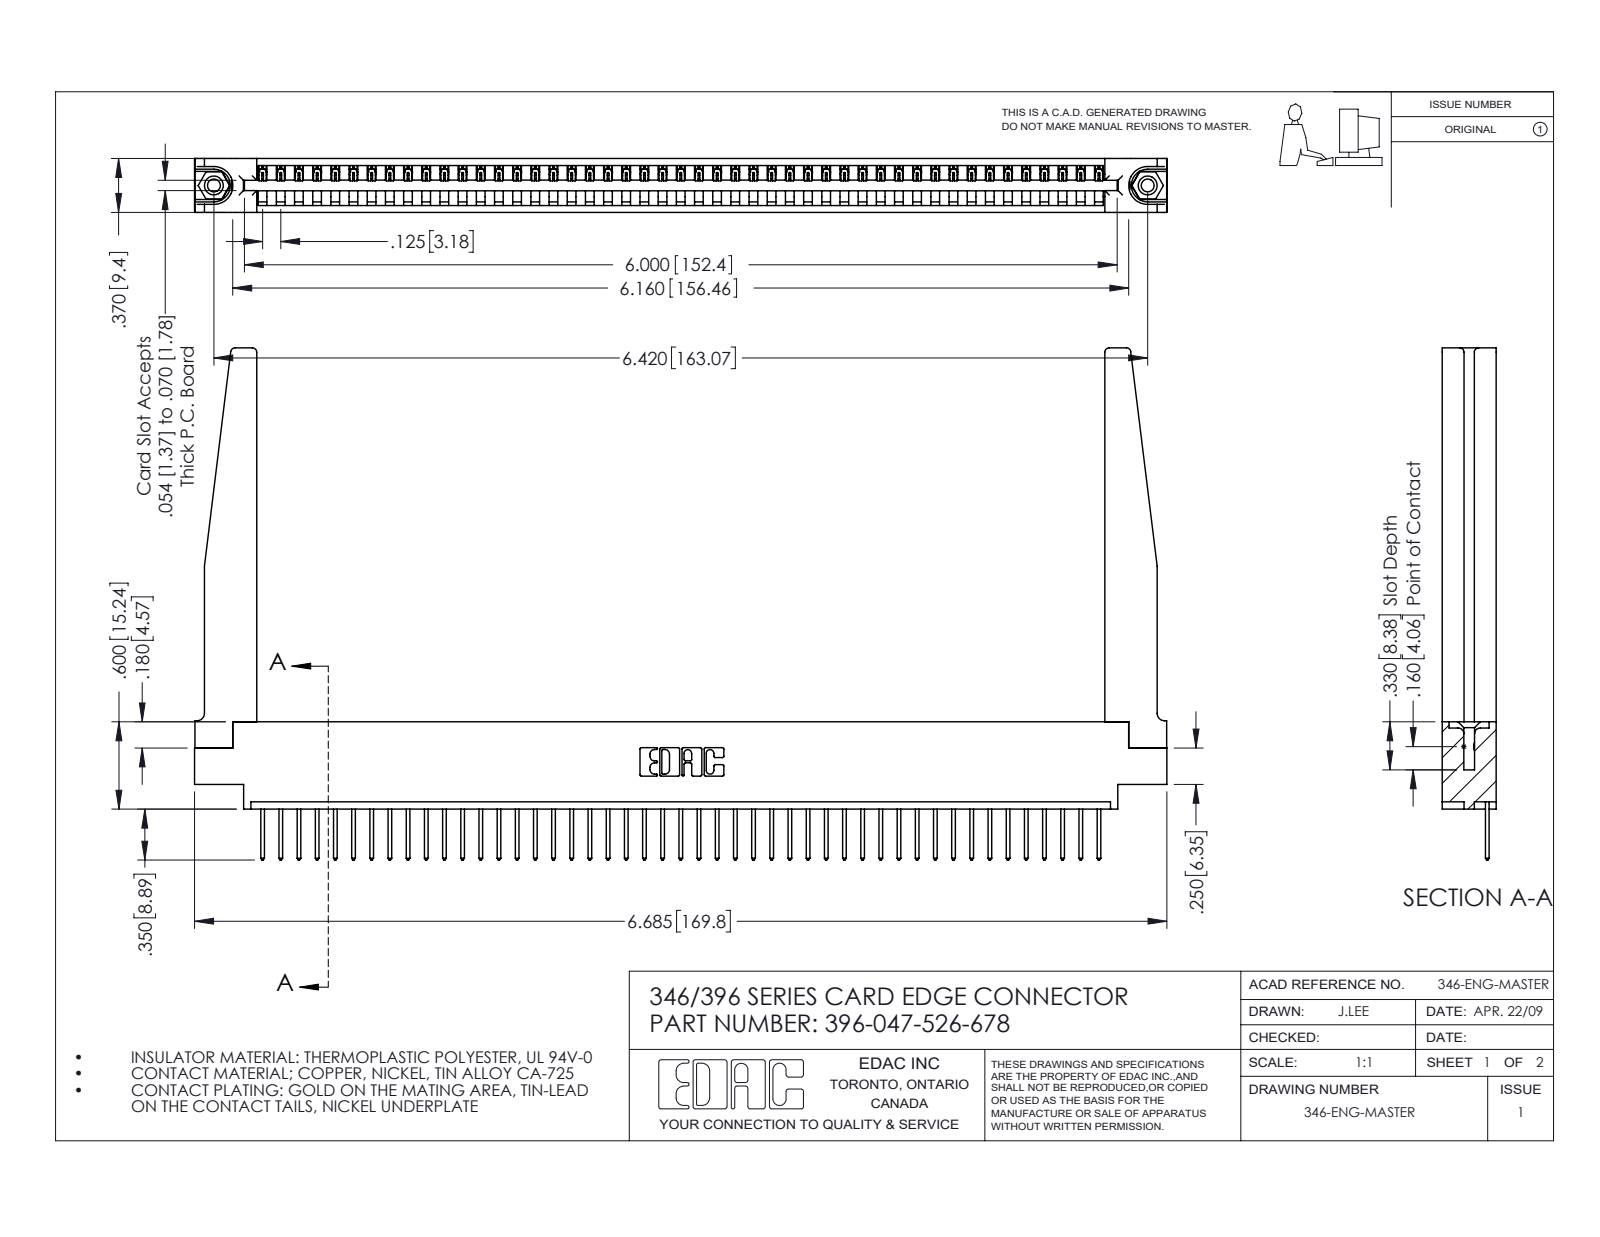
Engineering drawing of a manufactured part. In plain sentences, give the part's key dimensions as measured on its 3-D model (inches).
The part is named "345-292-001_345-293-126; 346 Part_0.170 Offset - 0.156 Dia-TH; 346-220-078_345-220-078; 396-047-526-678 (+1 more)". Its 3-D file was written by "SolidWorks 2016 (CONFIG_CONTROL_DESIGN)". It is 52 solids with 3086 faces: 2102 planar, 932 cylindrical and 52 other. Overall it measures 6.685 by 3.52 by 0.37 inches. Its volume is 1.404 cubic inches and its surface area 41.58 square inches. Round holes: 2 of diameter 0.089, 2 of diameter 0.125, 2 of diameter 0.156, 1 of diameter 0.064. Round bosses or shafts: 2 of diameter 0.155. Partial cylindrical surfaces (rounded edges, fillets, slot ends): 94 of radius 0.006, 94 of radius 0.01, 22 of radius 0.01, 8 of radius 0.03, 6 of radius 0.007, 6 of radius 0.031, 3 of radius 0.026, 2 of radius 0.031. The main face-to-face distances are 0.37, 0.048, 0.322, 0.072, 0.148, 0.25, 0.15, 0.298, 0.025, 0.222. The hole center spacings are 0.246, 6.211, 6.42.
